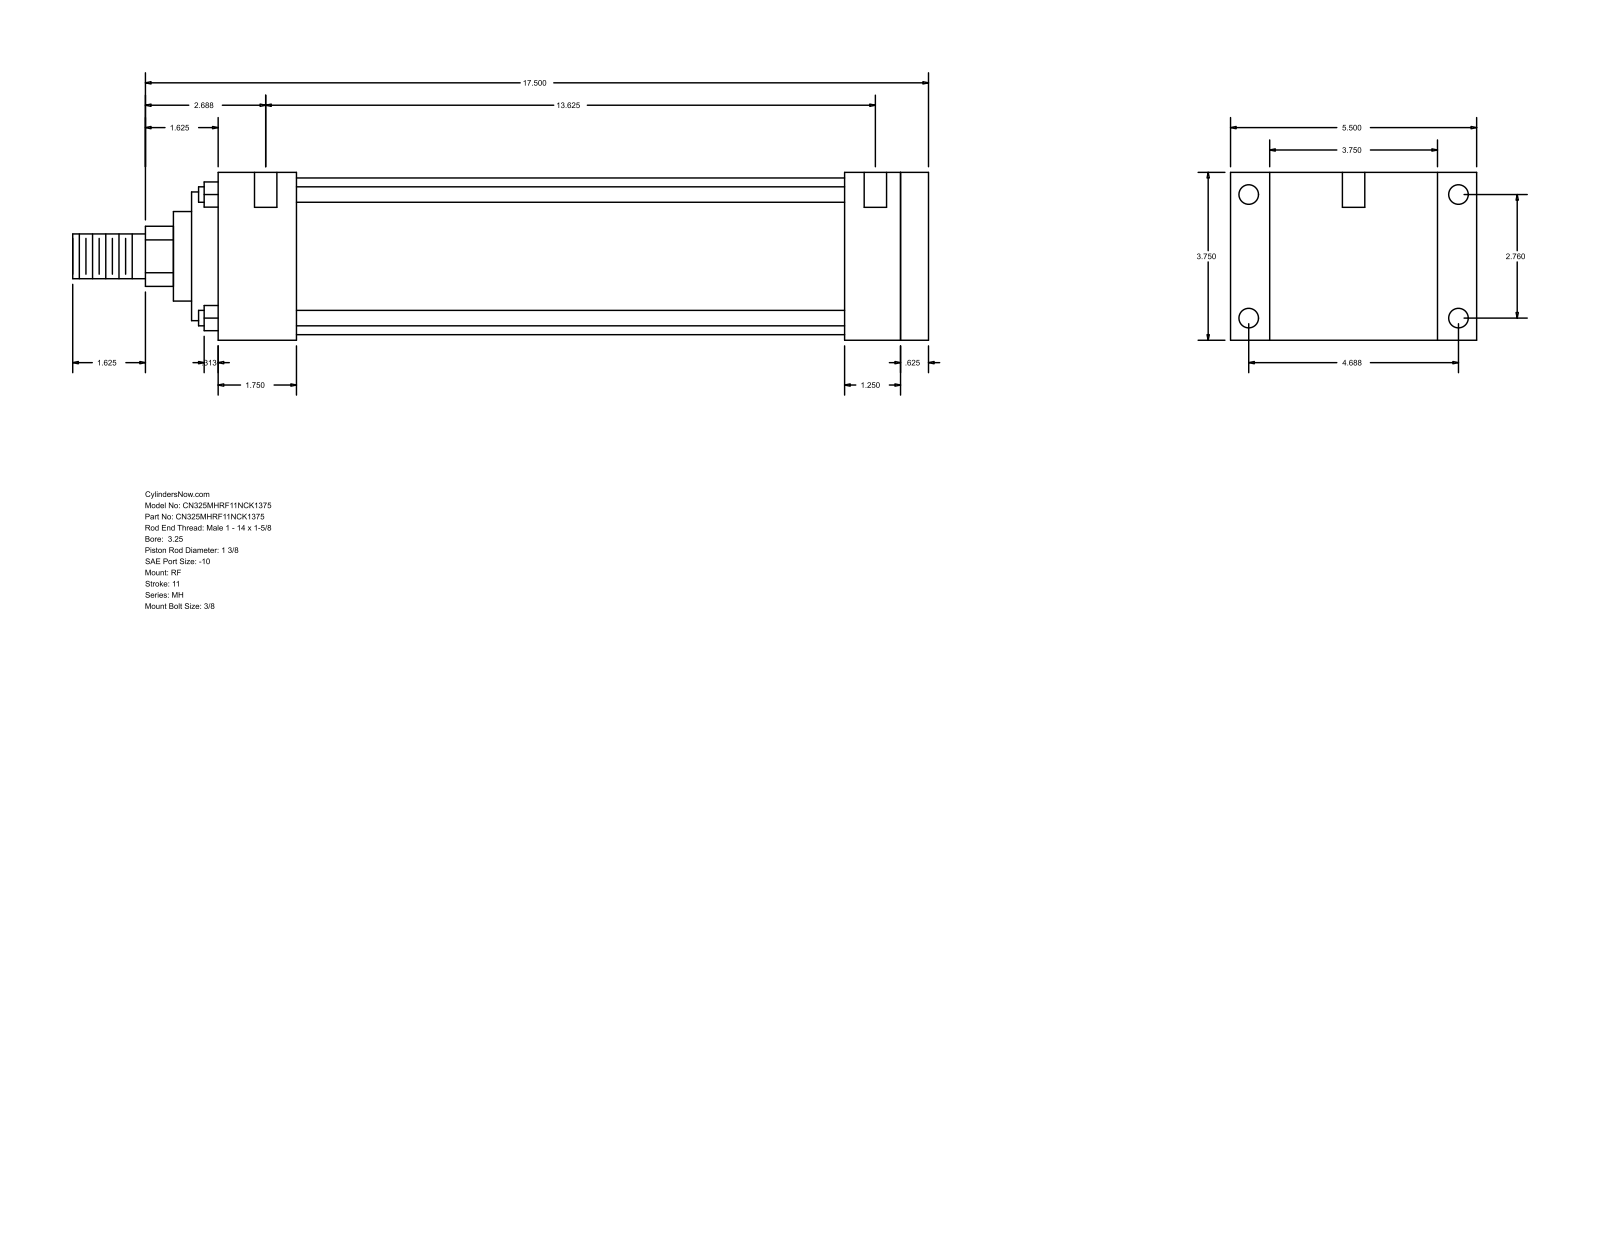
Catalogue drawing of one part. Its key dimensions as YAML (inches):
part_name: "MH_RF__0325_1.375"
step_written_by: "GSSL Pune (CONFIG_CONTROL_DESIGN)"
units: inches
bodies: {solids: 0, faces: 94, planar: 65, cylindrical: 29, other: 0}
overall_size: [19.125, 5.5, 3.75]
round_holes:
  - {diameter: 0.219, count: 4}
  - {diameter: 0.438, count: 4}
  - {diameter: 0.5, count: 2}
round_bosses_or_shafts:
  - {diameter: 0.345, count: 4}
  - {diameter: 3.5, count: 1}
  - {diameter: 2.875, count: 1}
  - {diameter: 2, count: 1}
  - {diameter: 1.375, count: 1}
  - {diameter: 1, count: 1}
partial_cylinders:
  - {radius: 0.672, count: 1}
face_to_face_distances: [3.75, 15.875, 0.625, 15.25, 0.875, 4.625, 1.75, 13.5, 14.125, 14]
hole_center_spacings: [2.76, 4.687, 5.439, 13.875, 0.063, 0.187, 13.625, 13.688]
